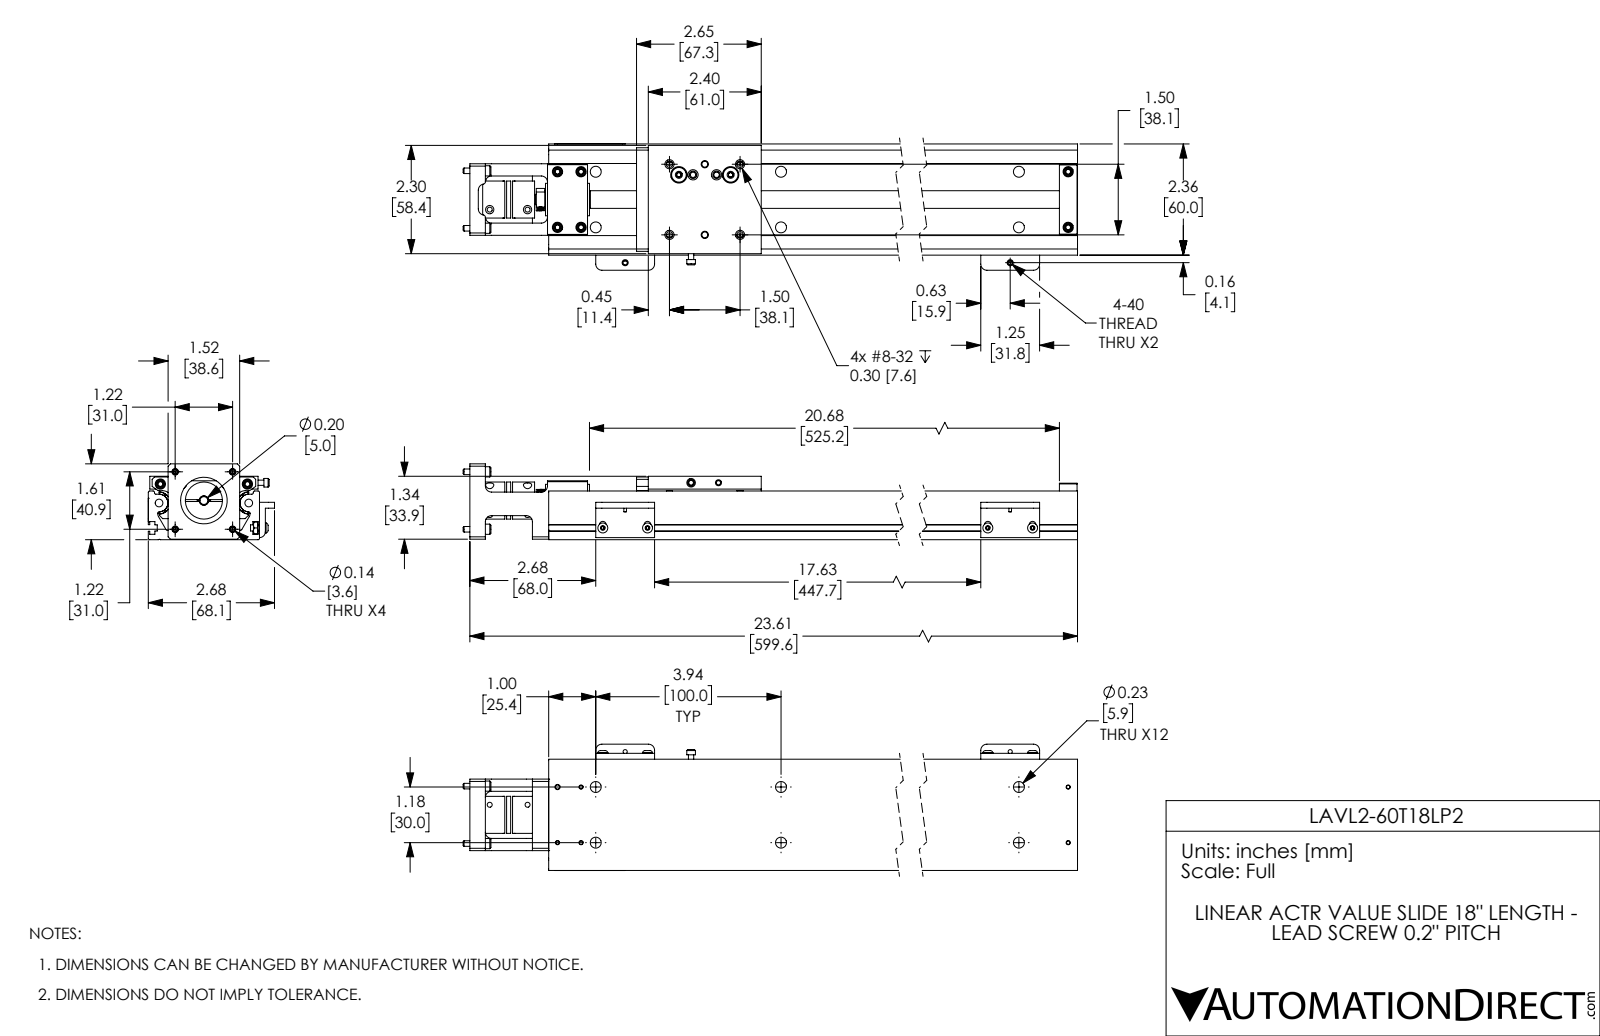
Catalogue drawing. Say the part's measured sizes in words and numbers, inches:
The part is named "LAVL2-60T18LP2; LAVL2-60T18LP2_BLOCK; LAVL2-60T18LP2_BODY". Its 3-D file was written by "SolidWorks 2017 (AUTOMOTIVE_DESIGN)". It is 52 solids with 2136 faces: 1295 planar, 533 cylindrical and 308 other. Overall it measures 23.748 by 2.683 by 1.612 inches. Its volume is 27.93 cubic inches and its surface area 369.6 square inches. Round holes: 18 of diameter 0.089, 12 of diameter 0.234, 10 of diameter 0.141, 10 of diameter 0.219, 6 of diameter 0.136, 4 of diameter 0.141, 2 of diameter 0.03, 2 of diameter 0.1, 2 of diameter 0.106, 2 of diameter 0.125, 2 of diameter 0.159, 2 of diameter 0.165. Round bosses or shafts: 15 of diameter 0.112, 11 of diameter 0.183, 4 of diameter 0.217, 4 of diameter 0.213, 4 of diameter 0.118, 2 of diameter 0.312, 2 of diameter 0.19, 2 of diameter 0.164. Partial cylindrical surfaces (rounded edges, fillets, slot ends): 20 of radius 0.13, 12 of radius 0.03, 8 of radius 0.07, 4 of radius 0.06, 3 of radius 0.02, 2 of radius 0.04, 2 of radius 0.05, 2 of radius 0.065. The main face-to-face distances are 0.2, 2.362, 0.14, 0.115, 0.185, 2.222, 0.11, 0.03, 2.332, 2.192. The hole center spacings are 3.937, 4.11, 1.181, 7.874, 7.962, 11.811, 11.87, 0.863.
